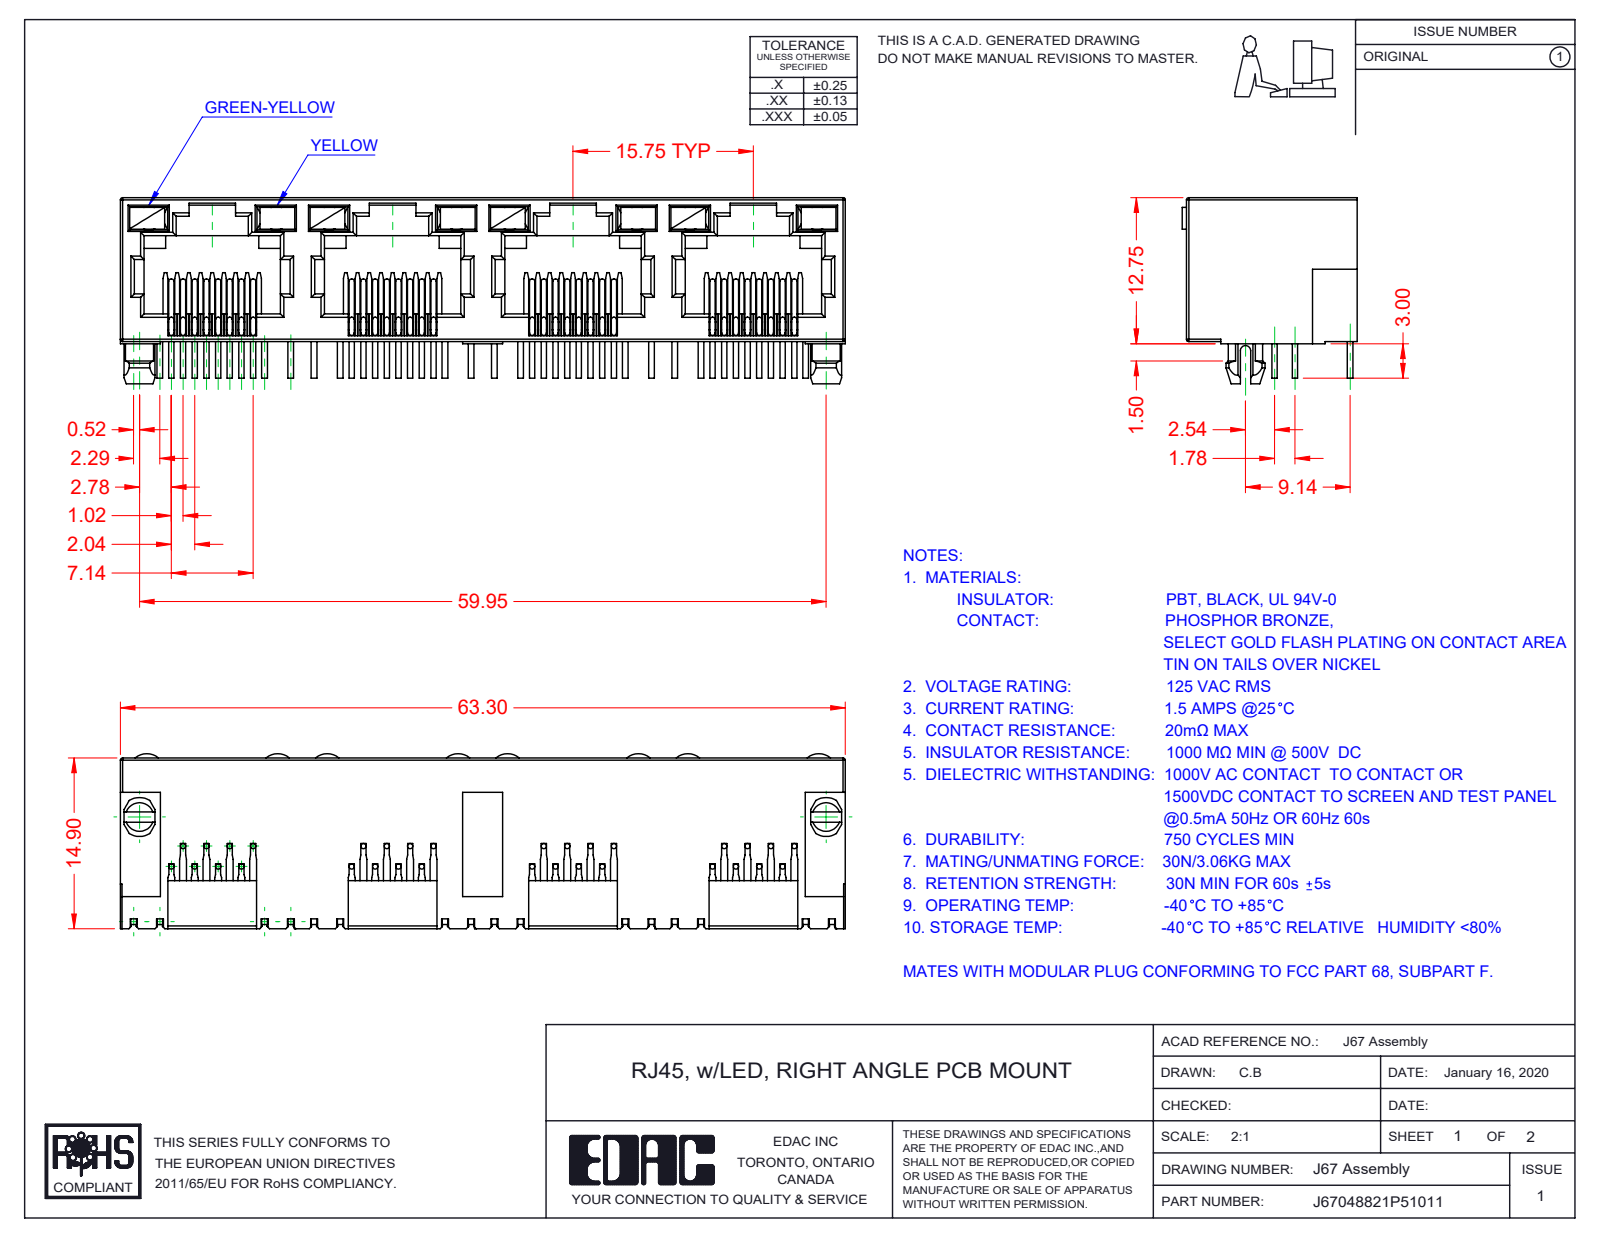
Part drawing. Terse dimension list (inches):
name: J67048822P51011; 67 LED RH_1-Yellow; 67 LED LH_5-Green-Yellow; 67 Insulator (+1 more)
written by: SolidWorks 2016 (CONFIG_CONTROL_DESIGN)
unit: in
bodies: 41 solids, 2473 faces (1781 planar, 484 cylindrical, 208 other)
size: 2.492 × 0.64 × 0.602
volume: 0.315 in³; area: 17.94 in²
bosses: 96× ⌀0.018
rounds: 66× R0.008, 29× R0.012, 9× R0.018, 8× R0.061, 2× R0.059, 2× R0.067, 1× R0.014, 1× R0.039
face distances: 0.02, 0.494, 0.074, 0.035, 0.394, 0.62, 0.039, 0.055, 0.433, 0.468
